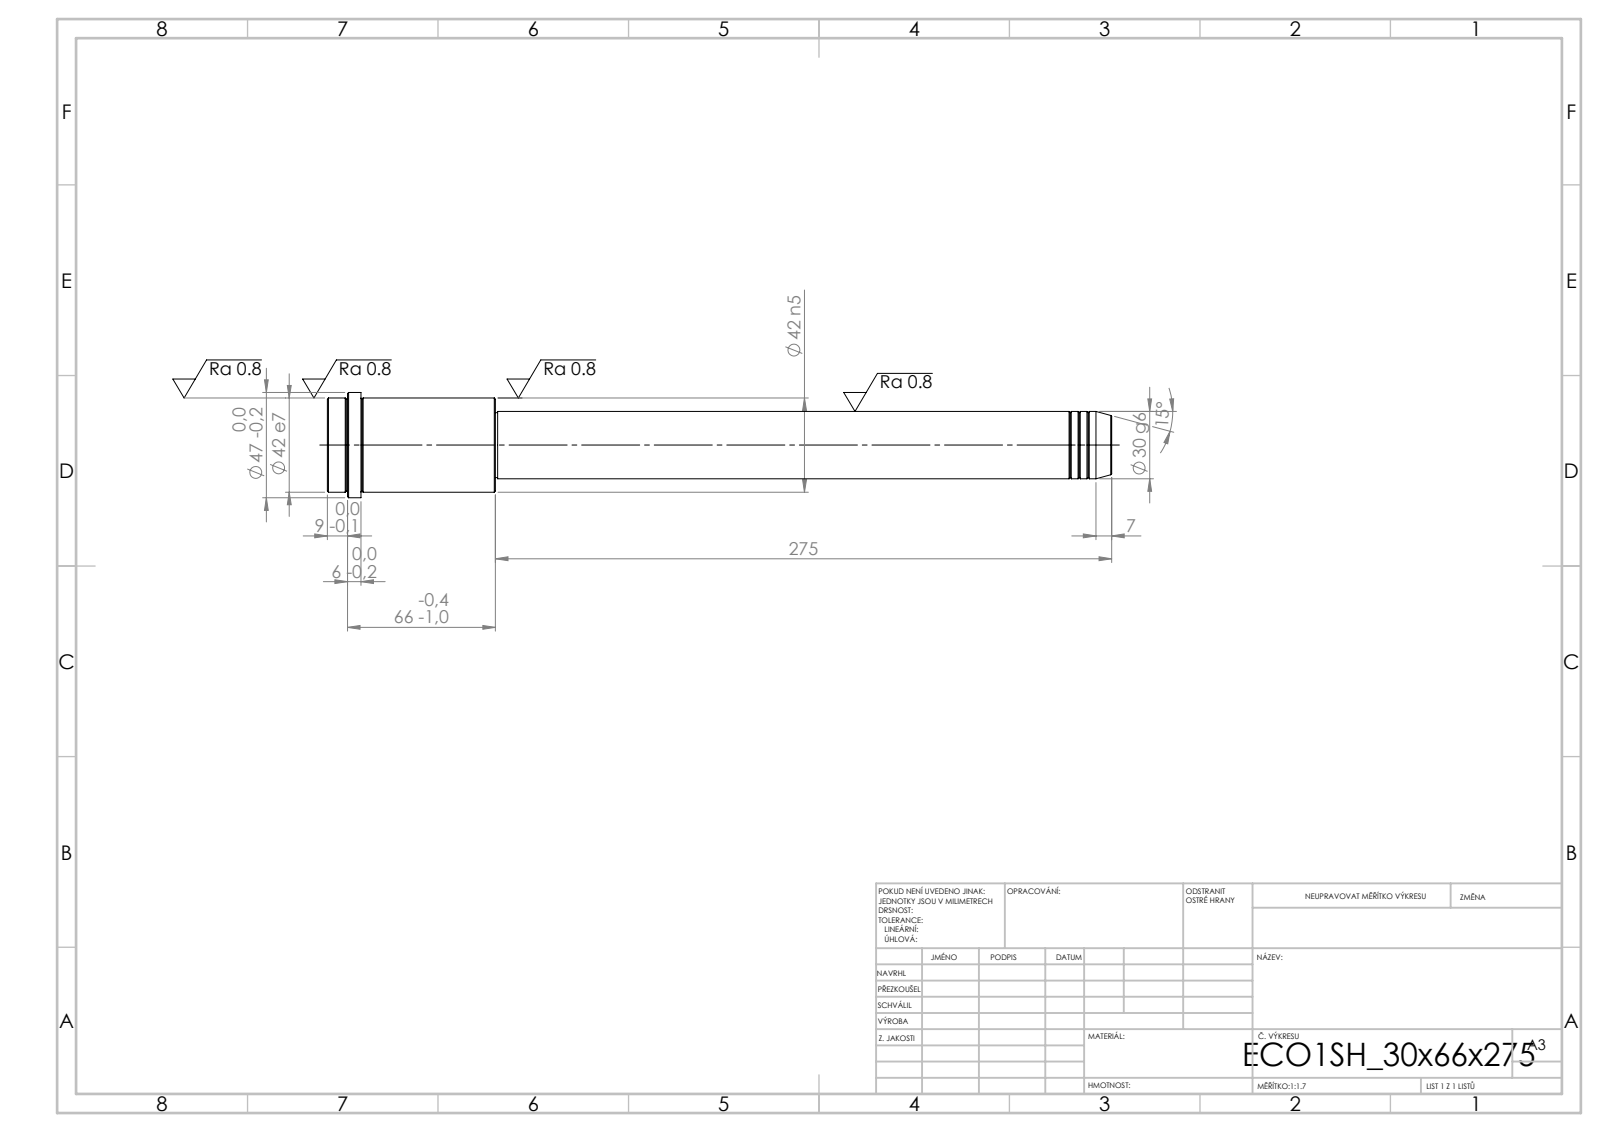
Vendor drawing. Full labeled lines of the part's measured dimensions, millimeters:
STEP written by: SolidWorks 2019 (CONFIG_CONTROL_DESIGN)
Units: millimetres
Bodies: 1 solid, 52 faces (6 planar, 16 cylindrical, 30 other)
Overall size (bounding box): 350 × 47 × 47
Volume: 299 487 mm³ · Surface area: 39 448 mm²
Round bosses / shafts (diameter × count): ⌀47 ×1, ⌀42 ×1, ⌀30 ×1, ⌀29 ×1
Main face-to-face distances: 75, 275, 350, 335, 60, 15, 341, 66, 6, 9
